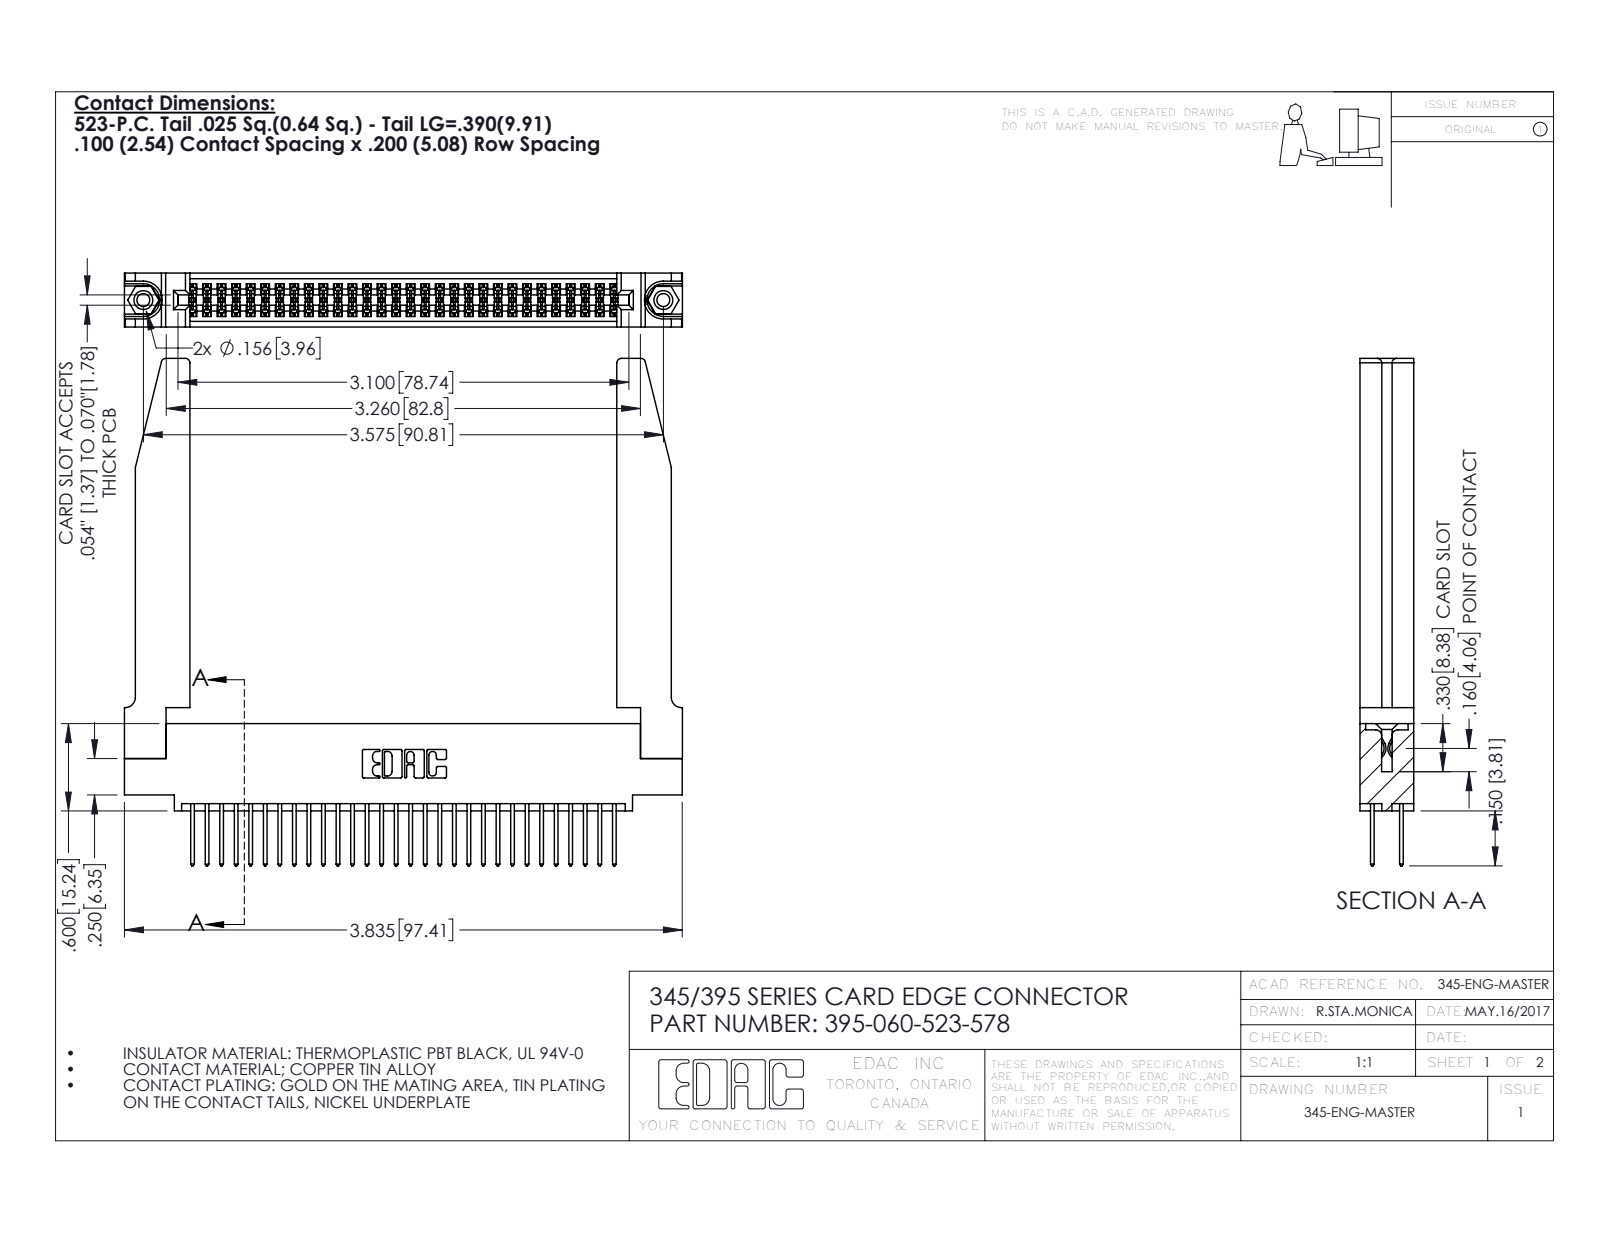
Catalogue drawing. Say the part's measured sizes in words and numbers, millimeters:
The part is named "345-292-001_345-293-123; 395-060-523-578; 345-250-001_345-250-001-102; 345 Part_0.110 Offset - 0.156 Dia-TH (+1 more)". Its 3-D file was written by "SolidWorks 2016 (CONFIG_CONTROL_DESIGN)". It is 65 solids with 3364 faces: 2206 planar, 1106 cylindrical and 52 other. Overall it measures 97.4 by 88.6 by 9.4 millimeters. Its volume is 17 170 cubic millimeters and its surface area 21 150 square millimeters. Round holes: 2 of diameter 2.3, 2 of diameter 3.2, 2 of diameter 4, 1 of diameter 1.6. Round bosses or shafts: 2 of diameter 3.9. Partial cylindrical surfaces (rounded edges, fillets, slot ends): 90 of radius 0.2, 60 of radius 0.3, 22 of radius 0.3, 8 of radius 0.8, 6 of radius 0.2, 6 of radius 0.8, 3 of radius 0.7, 2 of radius 0.4. The main face-to-face distances are 9.4, 1.8, 7.6, 5.1, 2.5, 6.9, 0.6, 5.7, 4.4, 3.8. The hole center spacings are 6.9, 84.8, 90.8.
